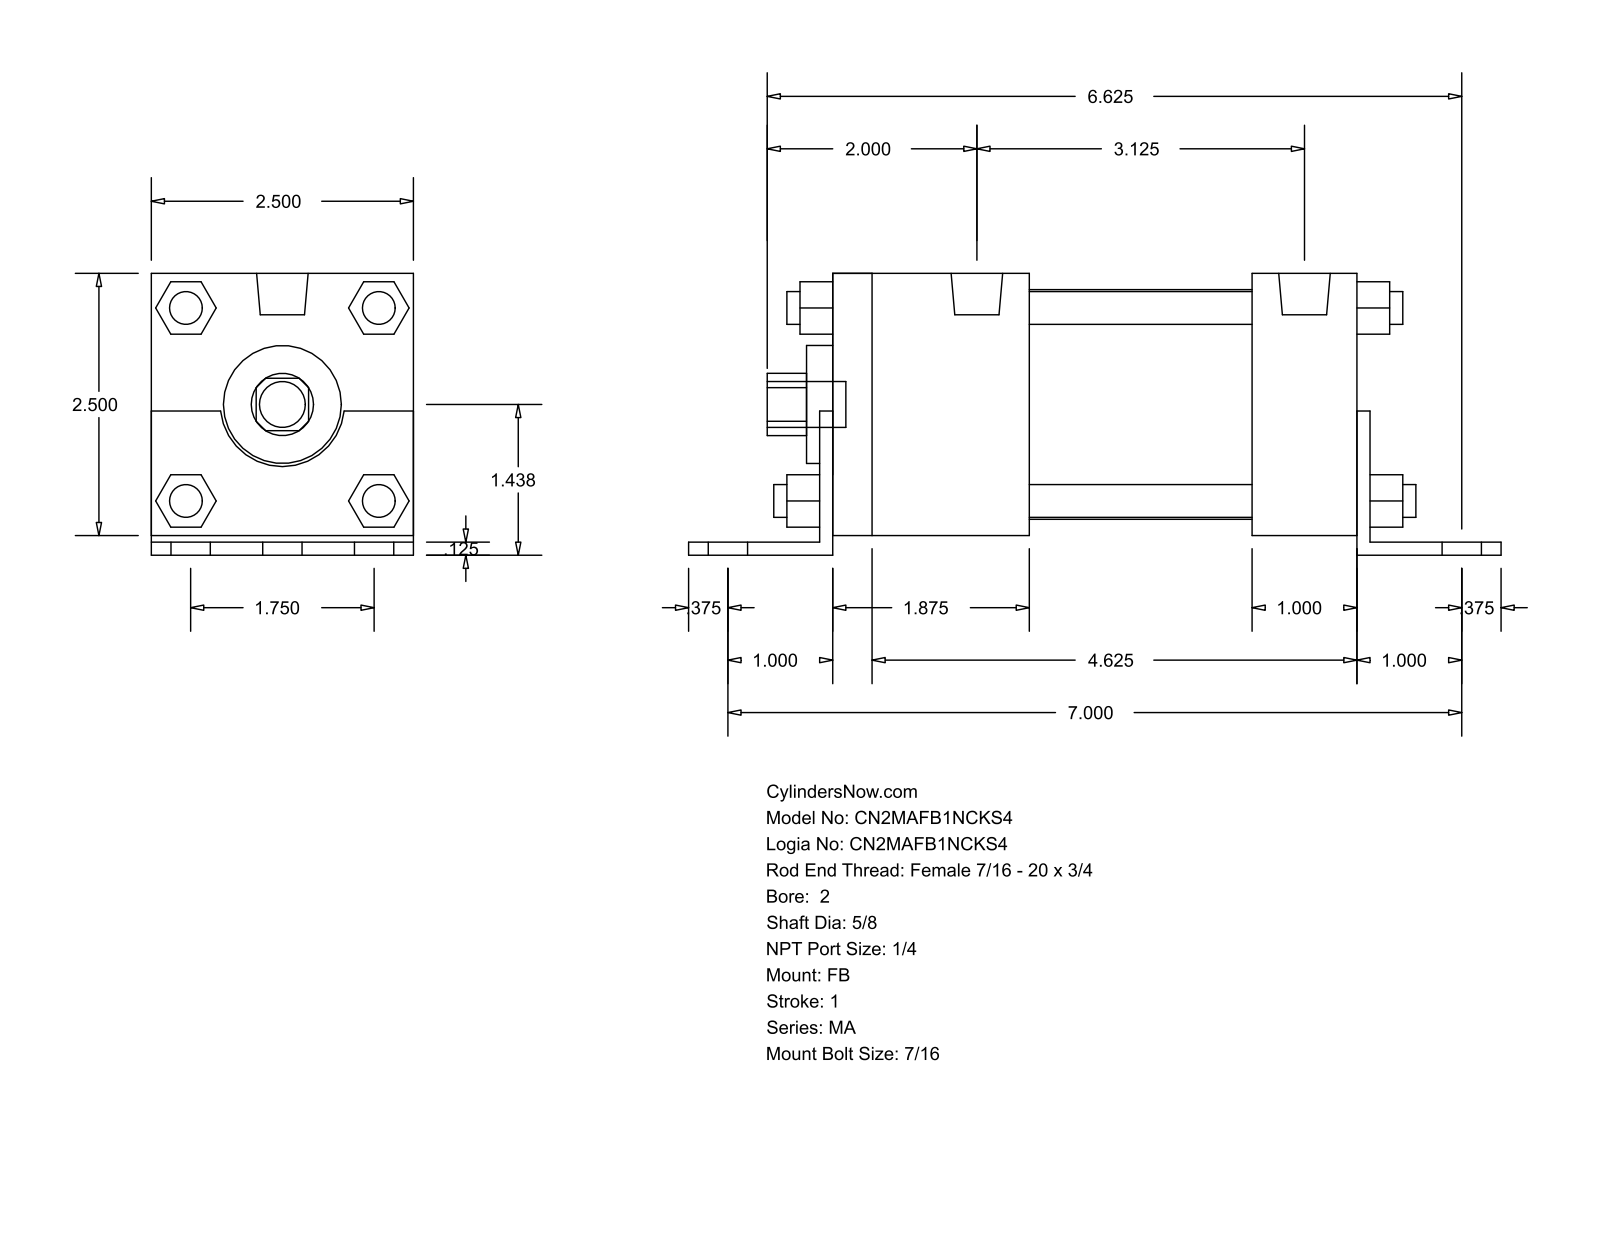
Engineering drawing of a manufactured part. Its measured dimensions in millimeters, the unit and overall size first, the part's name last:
Units: millimetres
Overall size (bounding box): 196.85 × 68.26 × 63.5
Round holes (diameter × count): ⌀15.88 ×1, ⌀28.57 ×1, ⌀55.63 ×1
Round bosses / shafts (diameter × count): ⌀7.94 ×8, ⌀11.11 ×7, ⌀12.49 ×2
Partial cylindrical surfaces — rounded edges, fillets, slot ends (radius × count): R7.54 ×1, R15.05 ×1
Main face-to-face distances: 63.5, 3.17, 4.76, 68.26, 1.59, 65.09, 127, 133.35, 53.97, 3.18
Bodies: 0 solids, 140 faces (105 planar, 35 cylindrical, 0 other)
Part name (STEP PRODUCT): MA_FB__0200_0.625
STEP written by: GSSL Pune (CONFIG_CONTROL_DESIGN)
